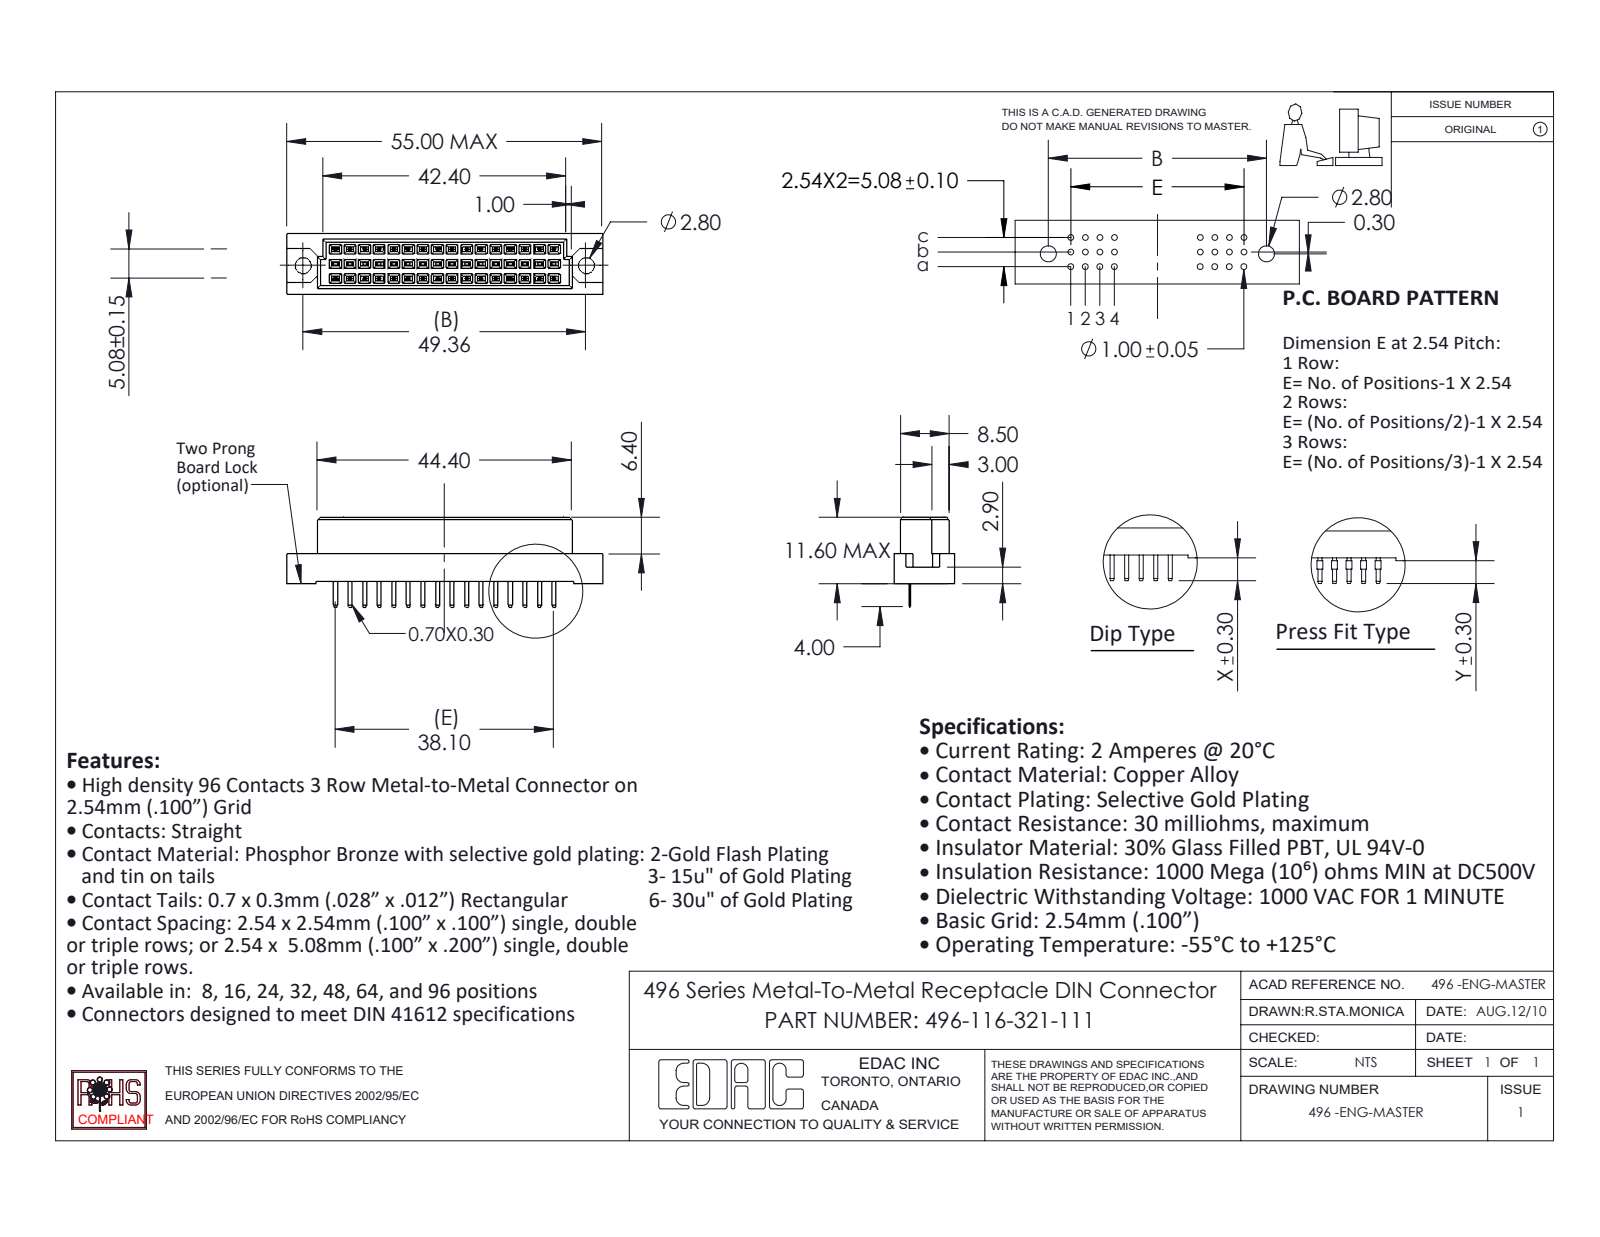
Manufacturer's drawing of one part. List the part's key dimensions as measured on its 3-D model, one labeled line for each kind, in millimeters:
Part name (STEP PRODUCT): 496 Part_48; 496-116-321-111; 496-290_21
STEP written by: SolidWorks 2020 (CONFIG_CONTROL_DESIGN)
Units: millimetres
Bodies: 17 solids, 826 faces (822 planar, 4 cylindrical, 0 other)
Overall size (bounding box): 55 × 15.6 × 10.6
Volume: 4 618 mm³ · Surface area: 4 487 mm²
Round holes (diameter × count): ⌀2.8 ×2
Main face-to-face distances: 2.54, 5.08, 1.05, 9.55, 0.81, 10.6, 3.35, 1.73, 8.5, 0.56
Hole centre spacings: 49.36
